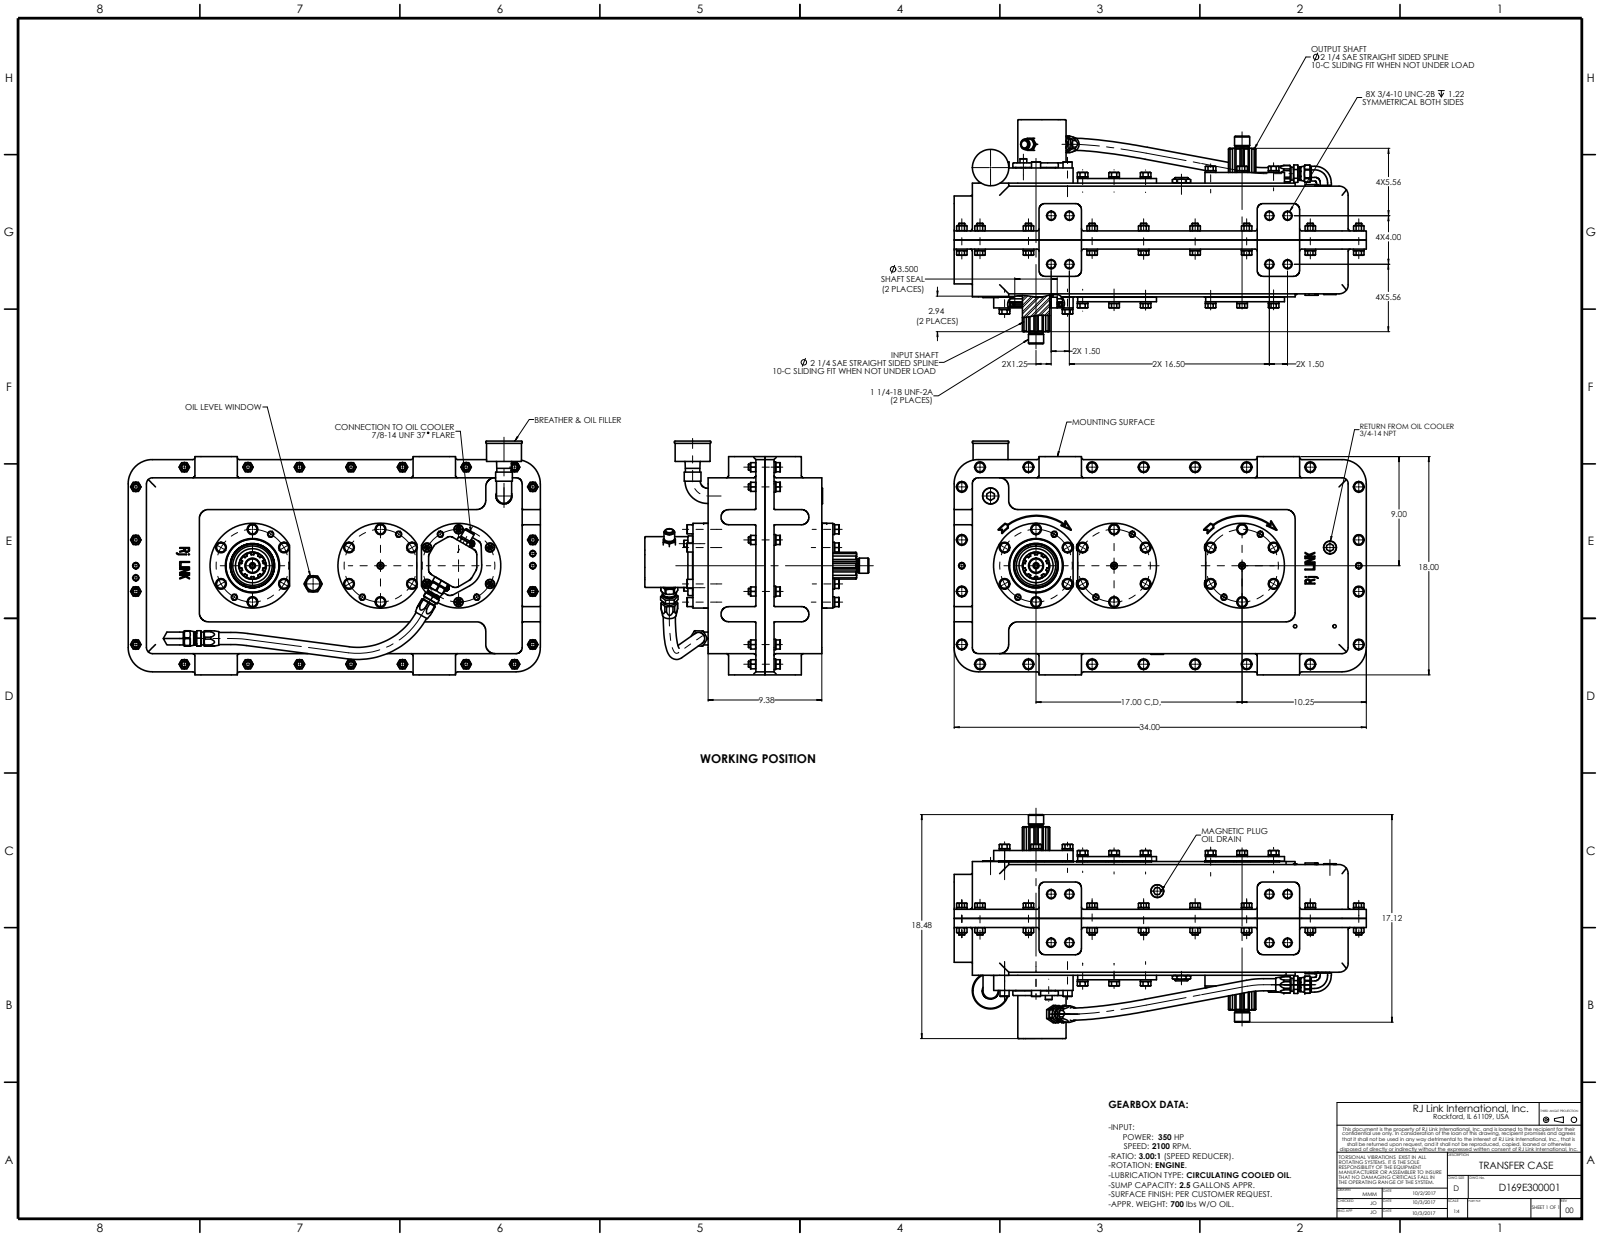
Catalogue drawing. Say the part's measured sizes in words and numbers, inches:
The part is named "HNZ_50-13_3; D169009; ME12-CTX-S_5; HHCSZ_50-13X1_5 (+8 more)". Its 3-D file was written by "SolidWorks 2017 (AUTOMOTIVE_DESIGN)". It is 117 solids with 6050 faces: 1905 planar, 2984 cylindrical and 1161 other. Overall it measures 34 by 19.28 by 18.479 inches. Its volume is 80.3 cubic inches and its surface area 6 556 square inches. Round holes: 40 of diameter 0.509, 40 of diameter 0.531, 30 of diameter 0.422, 22 of diameter 0.5, 8 of diameter 0.656, 5 of diameter 0.312, 4 of diameter 0.438, 4 of diameter 0.922, 3 of diameter 0.625, 3 of diameter 5.03, 2 of diameter 0.203, 2 of diameter 0.5. Round bosses or shafts: 48 of diameter 0.5, 40 of diameter 0.873, 40 of diameter 0.749, 40 of diameter 0.438, 22 of diameter 0.748, 14 of diameter 0.75, 7 of diameter 0.375, 6 of diameter 0.47. Partial cylindrical surfaces (rounded edges, fillets, slot ends): 94 of radius 0.18, 52 of radius 0.25, 40 of radius 0.016, 40 of radius 0.5, 32 of radius 0.029, 22 of radius 0.06, 14 of radius 0.75, 12 of radius 0.023. The main face-to-face distances are 4.69, 0.5, 0.75, 3.94, 0.25, 1.38, 8, 3.31, 14, 9.13. The hole center spacings are 3, 5.196, 8.102, 9.162, 14.48, 17.263, 19.656, 6.
